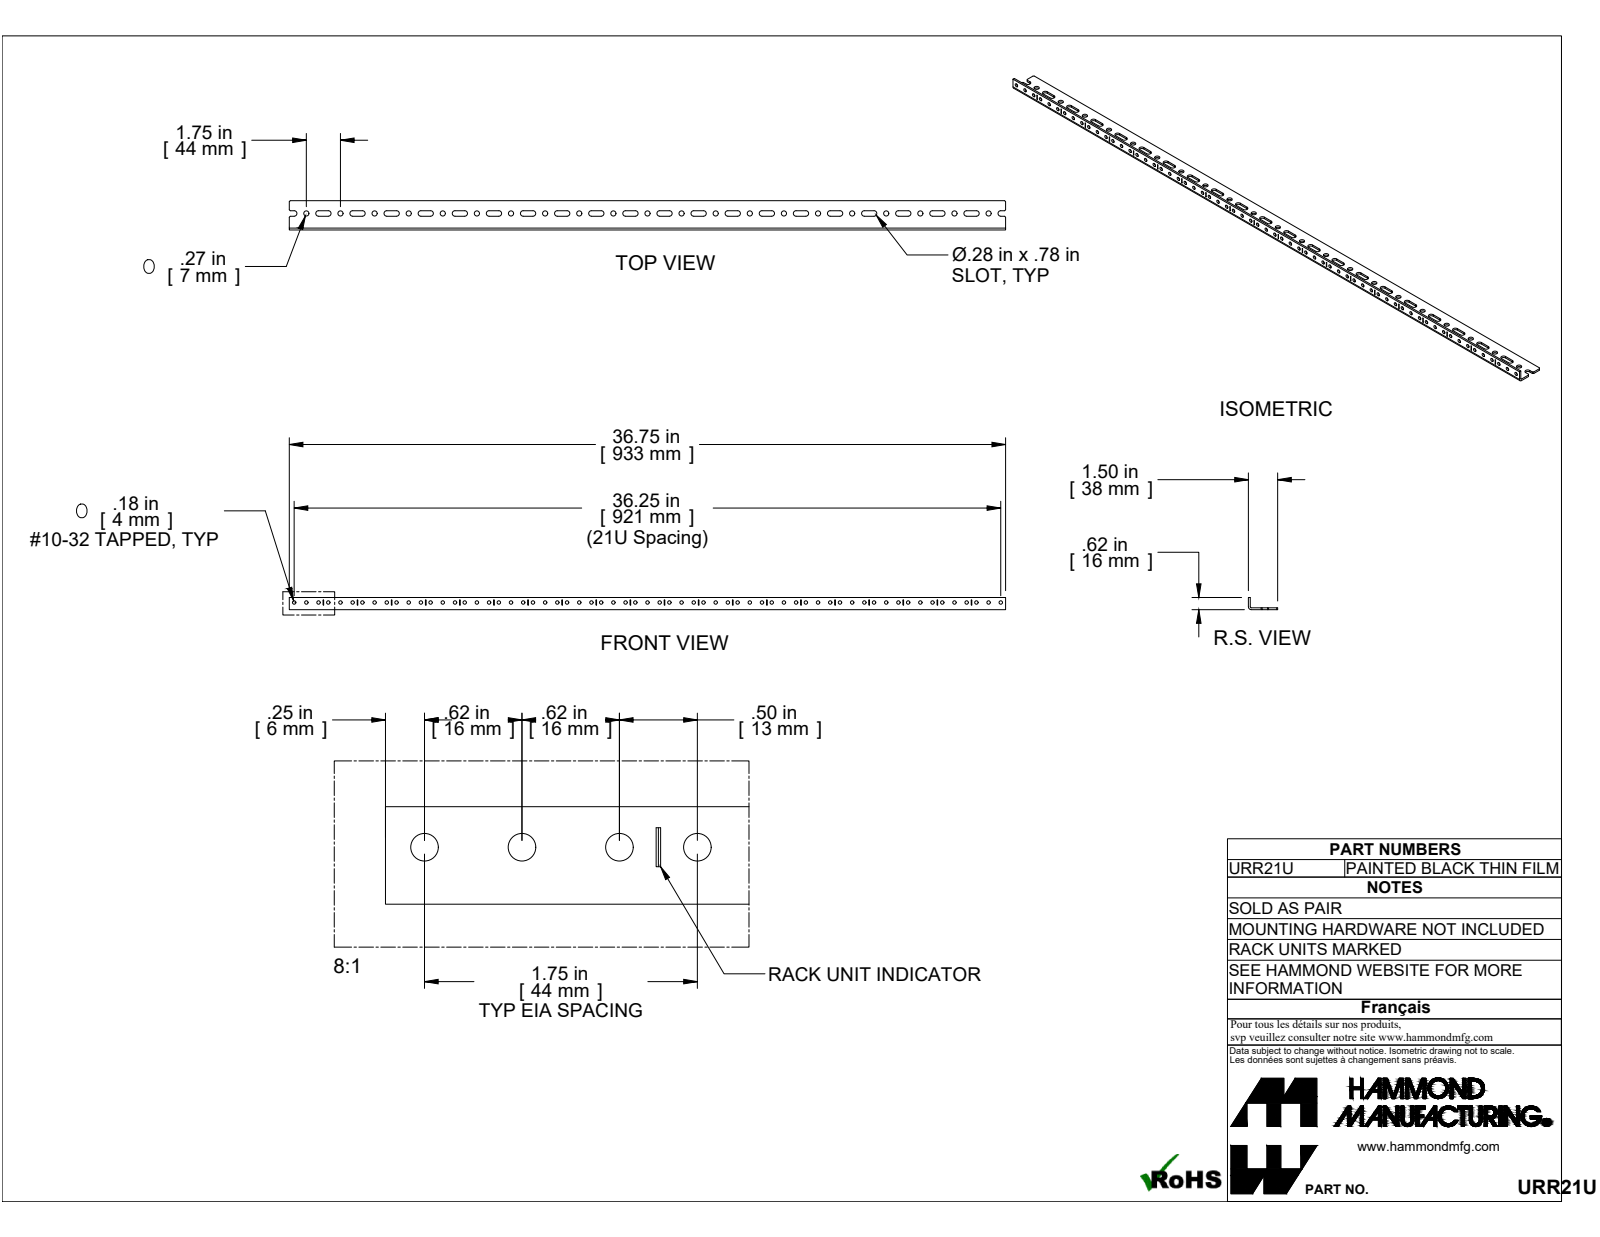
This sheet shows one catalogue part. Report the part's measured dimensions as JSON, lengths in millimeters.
{"part_name": "COM57213-21", "step_written_by": "ST-DEVELOPER v16.7 (AUTOMOTIVE_DESIGN)", "units": "millimeters", "bodies": {"solids": 1, "faces": 268, "planar": 140, "cylindrical": 128, "other": 0}, "overall_size": [933.45, 38.1, 15.88], "volume_mm3": 102902, "surface_area_mm2": 95766, "round_holes": [[4.5, 63], [6.76, 21]], "partial_cylinders_radius": [[3.57, 42], [1.22, 1], [3.63, 1]], "face_to_face_distances": [2.41, 15.88, 13.47, 38.1, 35.69, 17.84, 24.98, 15.43, 22.57, 7.14], "hole_center_spacings": [44.45, 88.9, 133.35, 177.8, 222.25, 266.7, 311.15, 355.6]}
